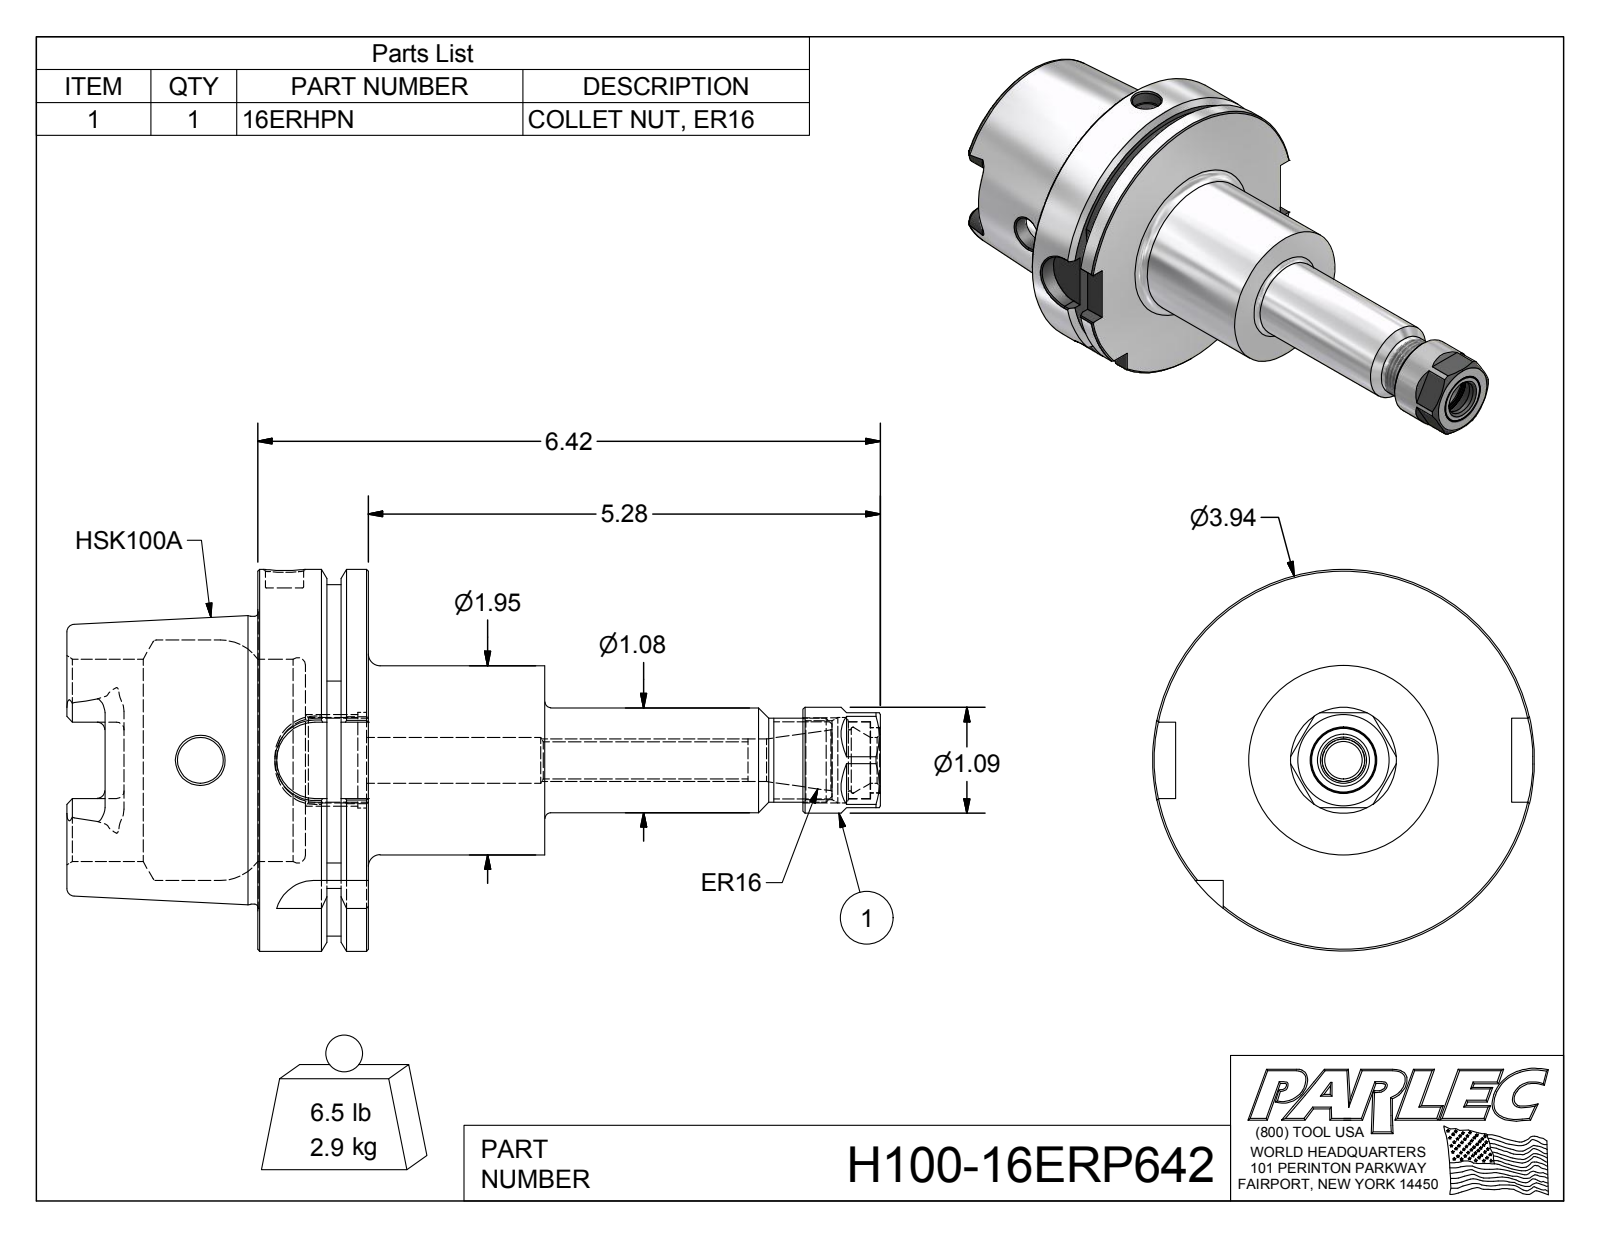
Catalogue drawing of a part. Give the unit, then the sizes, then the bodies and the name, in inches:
Units: inches
Overall size (bounding box): 8.389 × 3.937 × 3.937
Round holes (diameter × count): ⌀0.472 ×2, ⌀0.383 ×1, ⌀0.394 ×1, ⌀0.44 ×1, ⌀0.472 ×1, ⌀0.474 ×1, ⌀0.63 ×1, ⌀0.674 ×1, ⌀0.68 ×1, ⌀0.794 ×1, ⌀0.814 ×1, ⌀0.881 ×1
Round bosses / shafts (diameter × count): ⌀3.937 ×1, ⌀2.967 ×1, ⌀1.95 ×1, ⌀1.092 ×1, ⌀1.08 ×1, ⌀0.866 ×1, ⌀0.79 ×1, ⌀0.67 ×1
Partial cylindrical surfaces — rounded edges, fillets, slot ends (radius × count): R0.079 ×6, R0.192 ×4, R0.394 ×4, R1.811 ×1
Main face-to-face distances: 1.142, 0.492, 0.65, 2.962, 2.47, 1.82, 1.969, 2.461, 3.11, 4.93
Volume: 23.04 in³ · Surface area: 111.5 in²
Bodies: 3 solids, 176 faces (65 planar, 47 cylindrical, 64 other)
Part name (STEP PRODUCT): H100-16ERP642; H100-16ER6-1; 16ERHPN
STEP written by: Autodesk Inventor 2012 (AUTOMOTIVE_DESIGN)
